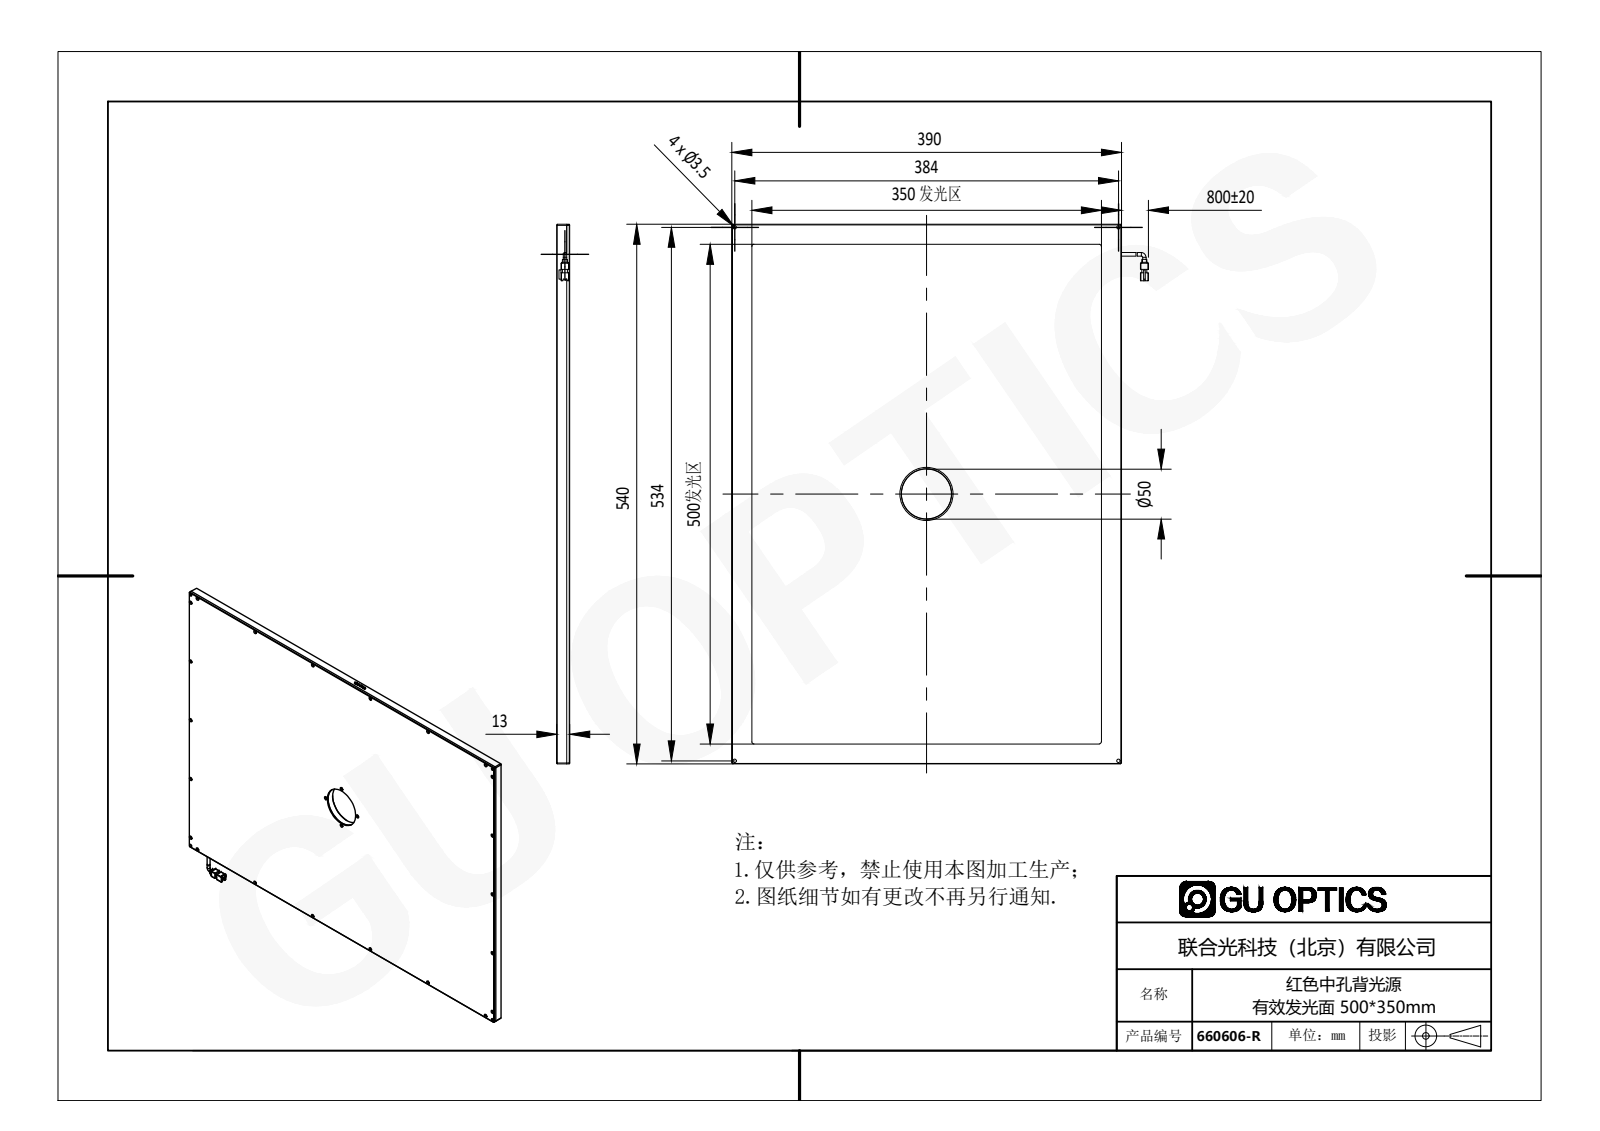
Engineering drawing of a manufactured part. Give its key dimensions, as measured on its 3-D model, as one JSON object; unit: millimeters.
{"part_name": "660606-R", "step_written_by": "SolidWorks 2016 (AUTOMOTIVE_DESIGN)", "units": "millimeters", "bodies": {"solids": 7, "faces": 987, "planar": 622, "cylindrical": 204, "other": 161}, "overall_size": [540, 417, 13], "volume_mm3": 2085000, "surface_area_mm2": 943357, "round_holes": [[2, 26], [1.6, 22], [2.4, 22], [3.5, 4], [50, 1], [53, 1], [60.2, 1]], "round_bosses_or_shafts": [[3.5, 2], [60, 1]], "partial_cylinders_radius": [[0.5, 8], [1, 6], [1.5, 4], [2, 4]], "face_to_face_distances": [6.5, 3, 9.5, 13, 3.5, 10, 2, 6, 8, 384], "hole_center_spacings": [102, 397.32, 12, 90, 204, 384, 434.82, 541.53]}
